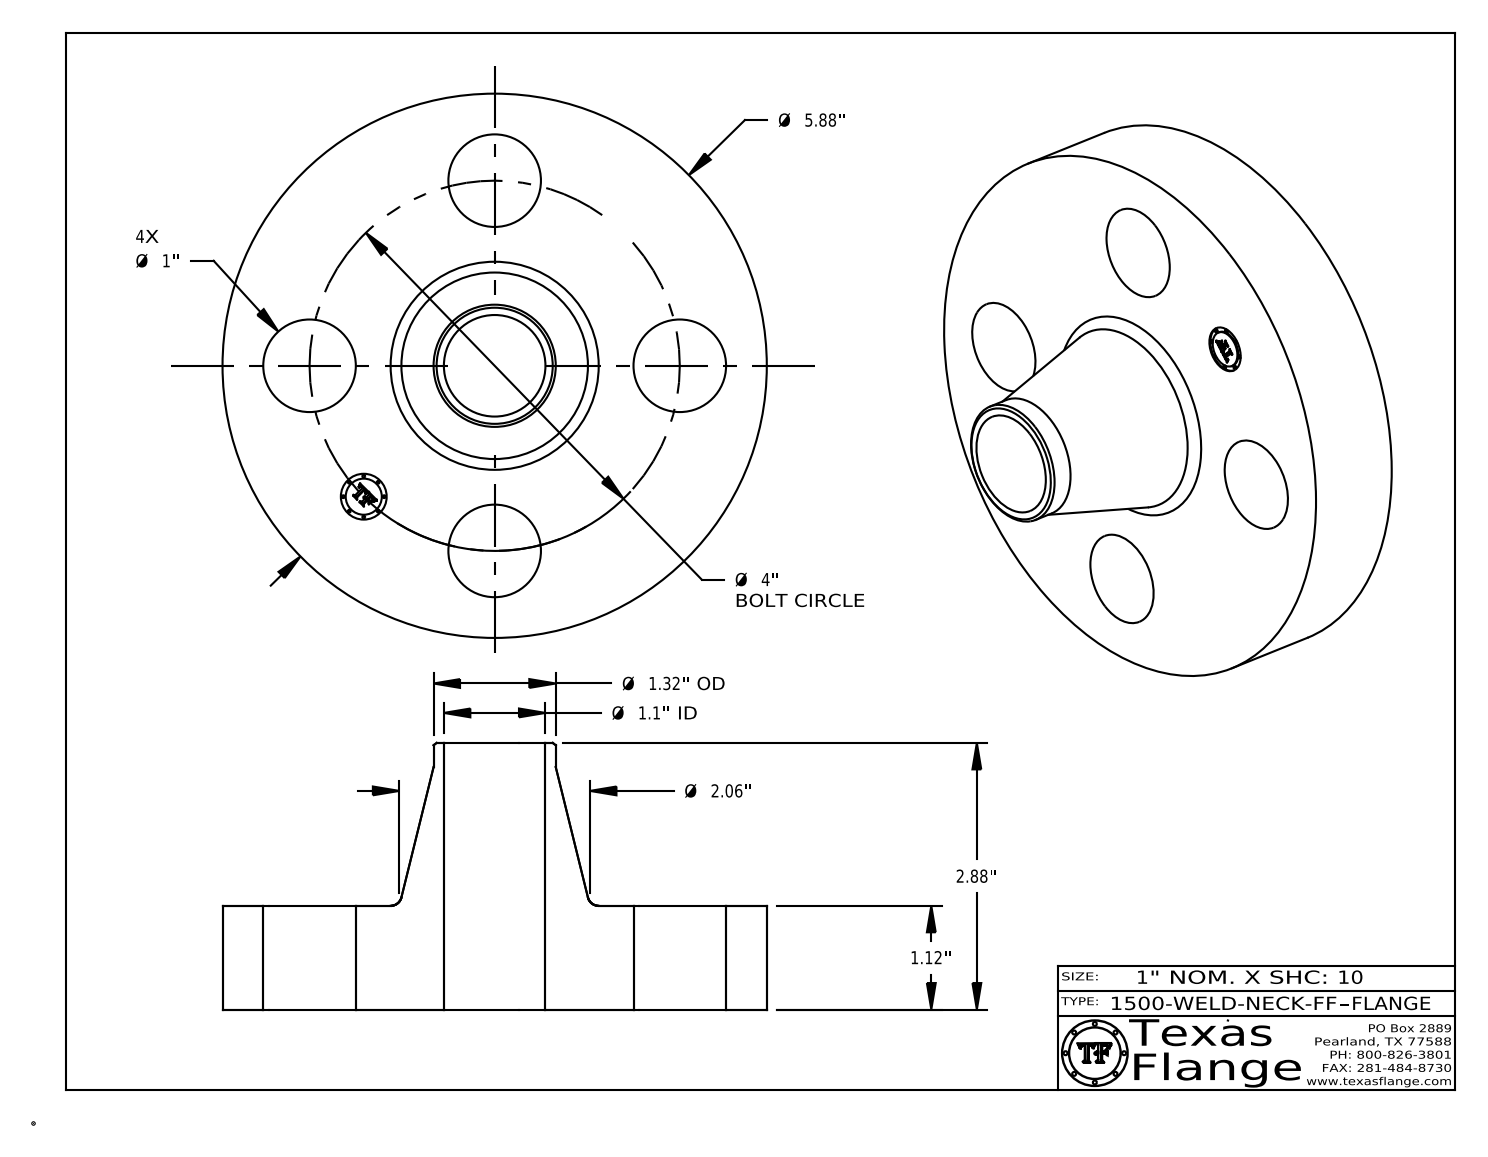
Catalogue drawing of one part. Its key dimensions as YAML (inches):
part_name: "1500-WELD-NECK-FF"
step_written_by: "CATIA V5 STEP AP214 (AUTOMOTIVE_DESIGN)"
units: inches
bodies: {solids: 1, faces: 408, planar: 368, cylindrical: 34, other: 6}
overall_size: [5.88, 5.88, 2.88]
volume: 27.95
surface_area: 97.98
round_holes:
  - {diameter: 1, count: 4}
  - {diameter: 0.495, count: 1}
  - {diameter: 1.097, count: 1}
round_bosses_or_shafts:
  - {diameter: 0.03, count: 8}
  - {diameter: 5.88, count: 1}
  - {diameter: 1.32, count: 1}
  - {diameter: 0.39, count: 1}
face_to_face_distances: [1.12, 2.88, 1.76, 0.015, 1.105, 1.775, 0.148, 0.145, 0.027, 0.096]
hole_center_spacings: [2, 2.828, 1.531, 3.695, 4]
